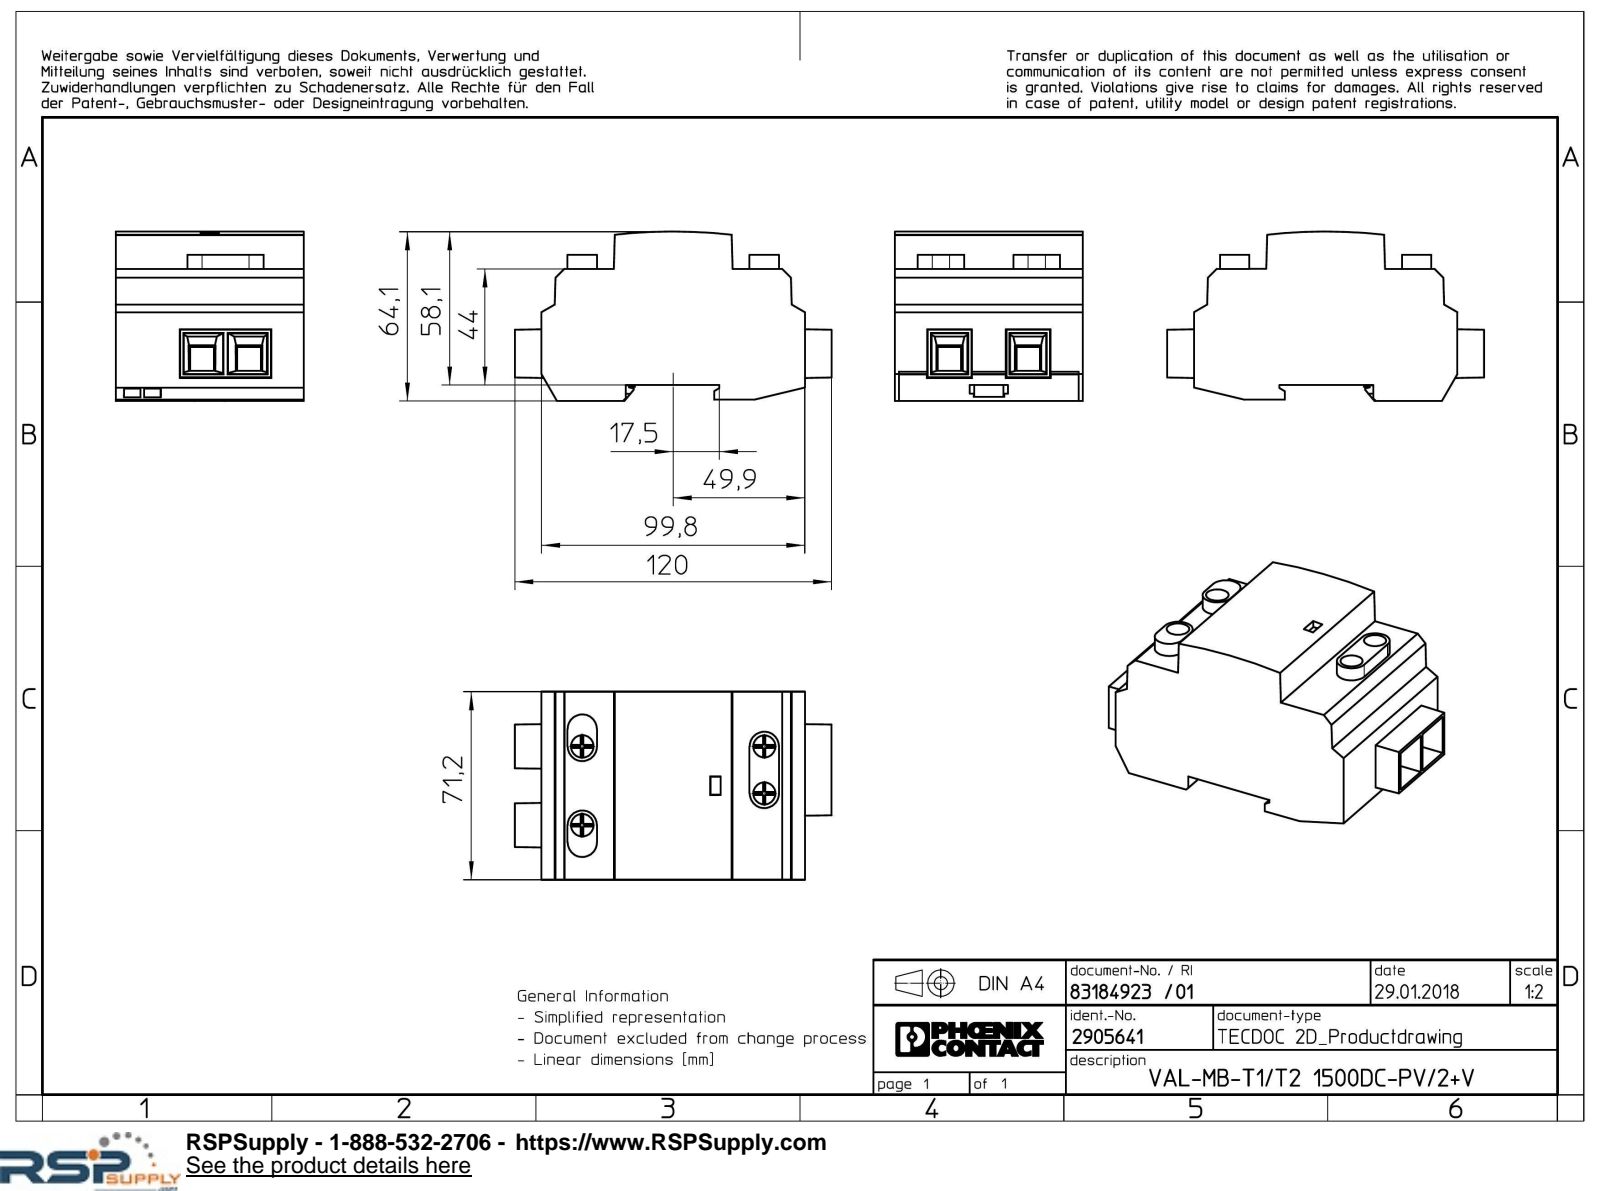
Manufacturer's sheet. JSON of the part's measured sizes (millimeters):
{"part_name": "VAL_MB_T1_T2...DC_PV_2_V-select", "step_written_by": "Creo Elements/Direct Modeling 18.1I 14-Aug-2016 (C) Parametric Technology GmbH (AUTOMOTIVE_DESIGN)", "units": "millimeters", "bodies": {"solids": 1, "faces": 314, "planar": 297, "cylindrical": 17, "other": 0}, "overall_size": [120, 71.2, 64.1], "volume_mm3": 353005, "surface_area_mm2": 47202, "round_holes": [[8.4, 2], [8.57, 2]], "round_bosses_or_shafts": [[2.3, 1]], "partial_cylinders_radius": [[5.57, 6], [200, 1]], "face_to_face_distances": [71.2, 44, 50, 6, 22.02, 5.5, 29.8, 49.5, 0.5, 99.8], "hole_center_spacings": [17.8, 29.8, 69, 70.04, 71.26, 75.16]}
